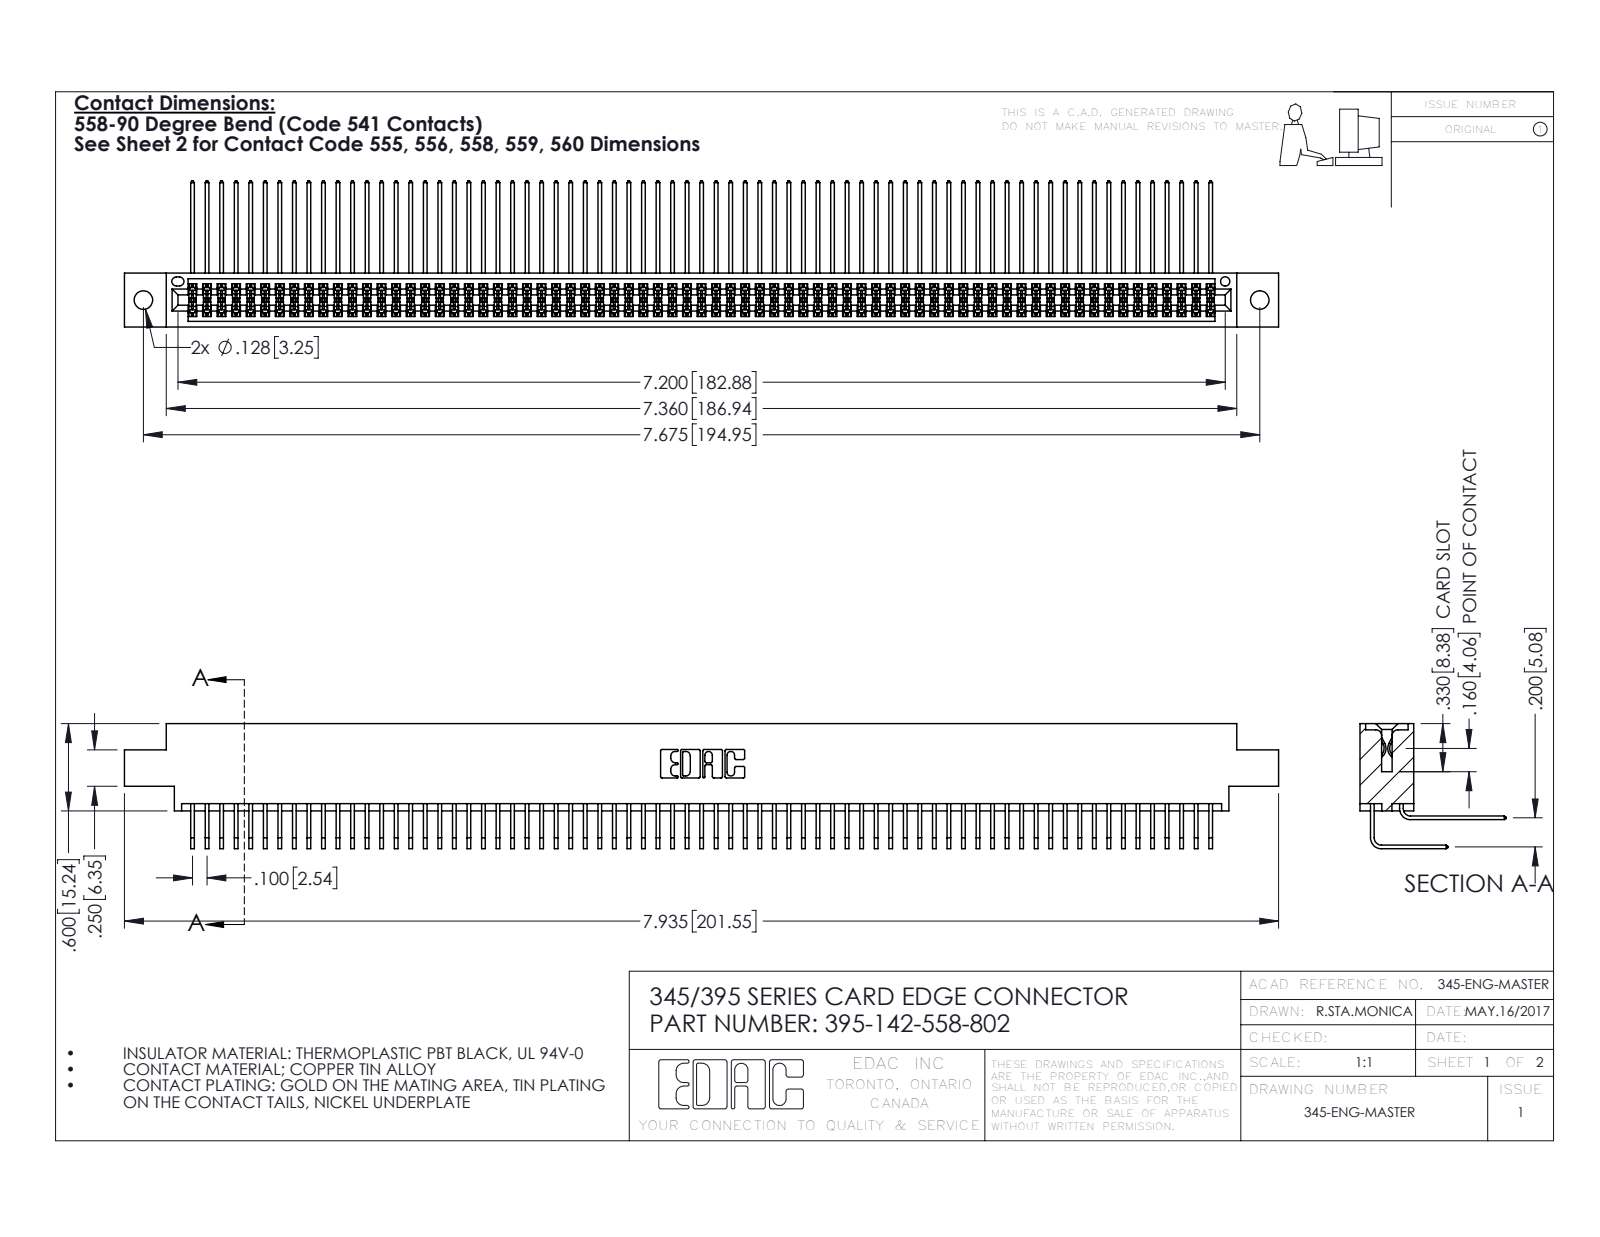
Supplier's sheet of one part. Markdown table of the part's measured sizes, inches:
| quantity | value |
| --- | --- |
| part name | 345 Part_0.170 Offset - 0.128 Dia; 395-142-558-802; 345-292-001_558 559 Tail - 1; 345-292-001_558 Tail - 2 |
| STEP written by | SolidWorks 2016 (CONFIG_CONTROL_DESIGN) |
| units | inches |
| bodies | 143 solids, 7514 faces (5054 planar, 2460 cylindrical, 0 other) |
| overall size | 7.935 × 1.005 × 0.859 |
| volume | 1.252 in³ |
| surface area | 53.65 in² |
| round holes (diameter × count) | 0.128 × 2, 0.064 × 1 |
| partial cylindrical surfaces (radius × count) | 0.006 × 283, 0.01 × 22, 0.007 × 6, 0.031 × 6, 0.026 × 3, 0.014 × 2, 0.019 × 2, 0.022 × 2 |
| main face-to-face distances | 0.072, 0.298, 0.2, 0.37, 0.098, 0.272, 0.025, 0.225, 0.175, 0.025 |
| hole center spacings | 0.27, 7.439, 7.675 |
